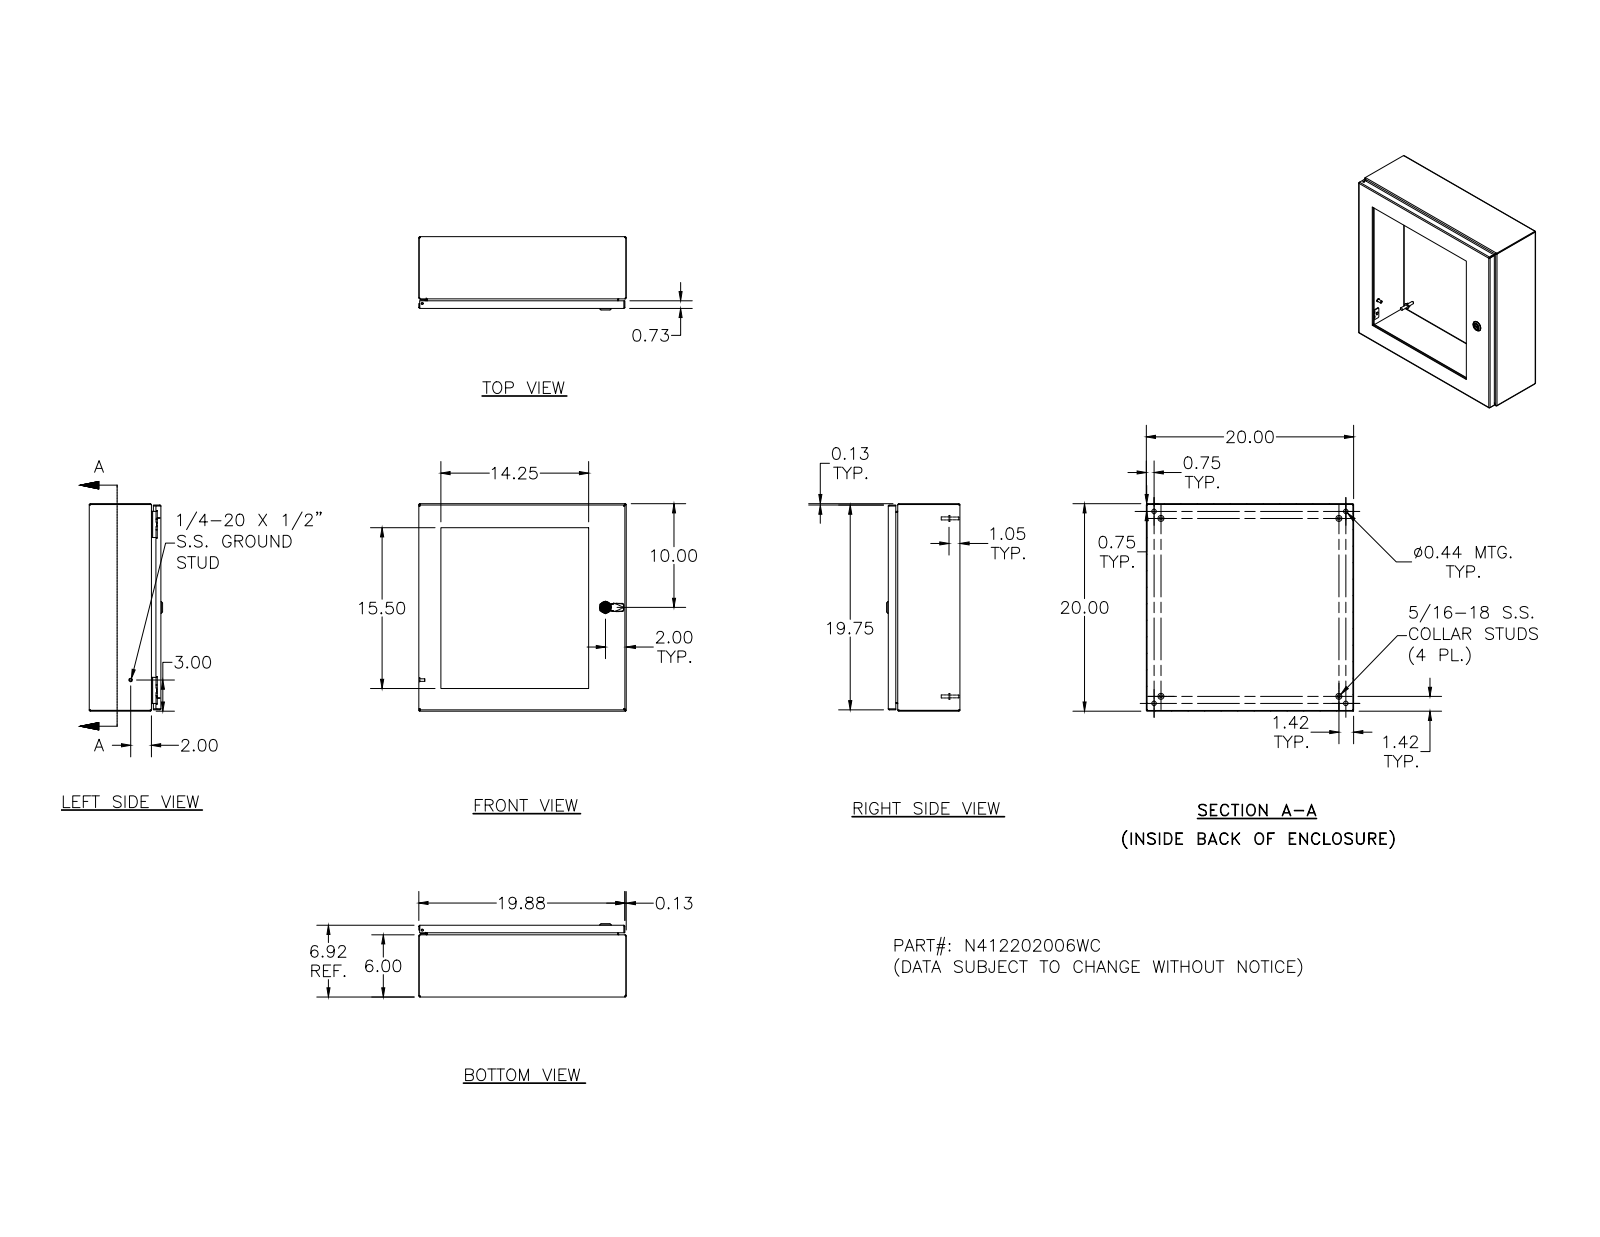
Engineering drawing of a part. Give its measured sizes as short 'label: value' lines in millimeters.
name: N412202006WC
written by: SolidWorks 2018 (AUTOMOTIVE_DESIGN)
unit: mm
bodies: 69 solids, 2019 faces (753 planar, 617 cylindrical, 649 other)
size: 508 × 508 × 179.7
volume: 2 602 000 mm³; area: 2 030 000 mm²
holes: 18× ⌀4, 16× ⌀7.1, 5× ⌀4.8, 4× ⌀2.4, 4× ⌀3.9, 4× ⌀4.2, 4× ⌀4.4, 4× ⌀11.1, 1× ⌀4.7, 1× ⌀5, 1× ⌀8, 1× ⌀10
bosses: 16× ⌀8.6, 16× ⌀4.8, 10× ⌀6.4, 4× ⌀14.3, 4× ⌀9.1, 4× ⌀8.1, 4× ⌀7.6, 4× ⌀7
rounds: 34× R0.8, 30× R0.3, 26× R1.3, 24× R2.7, 18× R0.4, 16× R3.2, 13× R0.5, 8× R0.8
face distances: 1.9, 173.8, 506.1, 171.9, 6.4, 167.5, 165.6, 508, 504.2, 175.7
hole spacings: 101.6, 203.2, 406.6, 406.4, 437.4, 158, 218.1, 254.9
